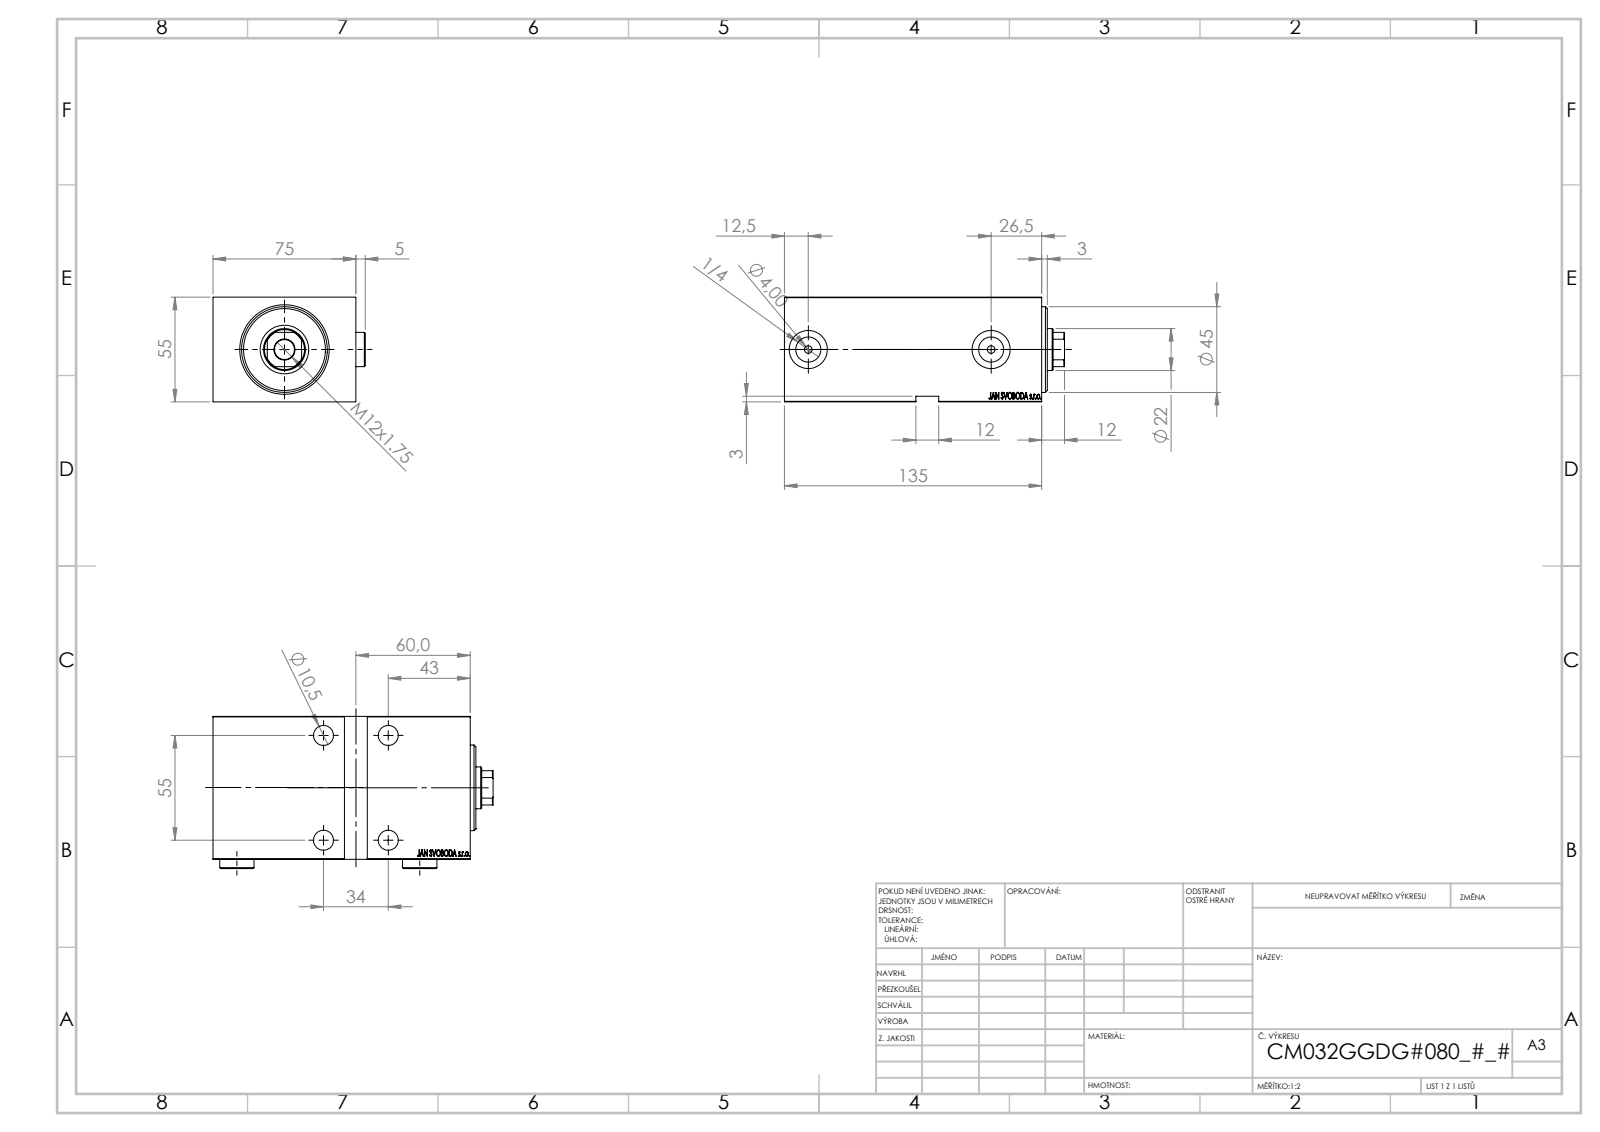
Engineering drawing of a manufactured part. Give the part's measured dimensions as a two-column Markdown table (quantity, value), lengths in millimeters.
| quantity | value |
| --- | --- |
| part name | V450CM_VC_G; V450CM_G_Body; V450CM_G_VCP |
| STEP written by | SolidWorks 2019 (CONFIG_CONTROL_DESIGN) |
| units | millimeters |
| bodies | 3 solids, 874 faces (416 planar, 64 cylindrical, 394 other) |
| overall size | 147 × 75 × 55 |
| volume | 484 765 mm³ |
| surface area | 86 171 mm² |
| round holes (diameter × count) | 10.5 × 5, 16.5 × 4, 4 × 2, 13.16 × 2, 20 × 2, 22 × 1, 25.5 × 1, 32 × 1, 34 × 1, 45 × 1 |
| round bosses / shafts (diameter × count) | 27 × 1 |
| partial cylindrical surfaces (radius × count) | 10.5 × 1 |
| main face-to-face distances | 55, 75, 135, 3, 5, 130, 10, 120, 125, 8 |
| hole center spacings | 34, 55, 64.66, 96 |
